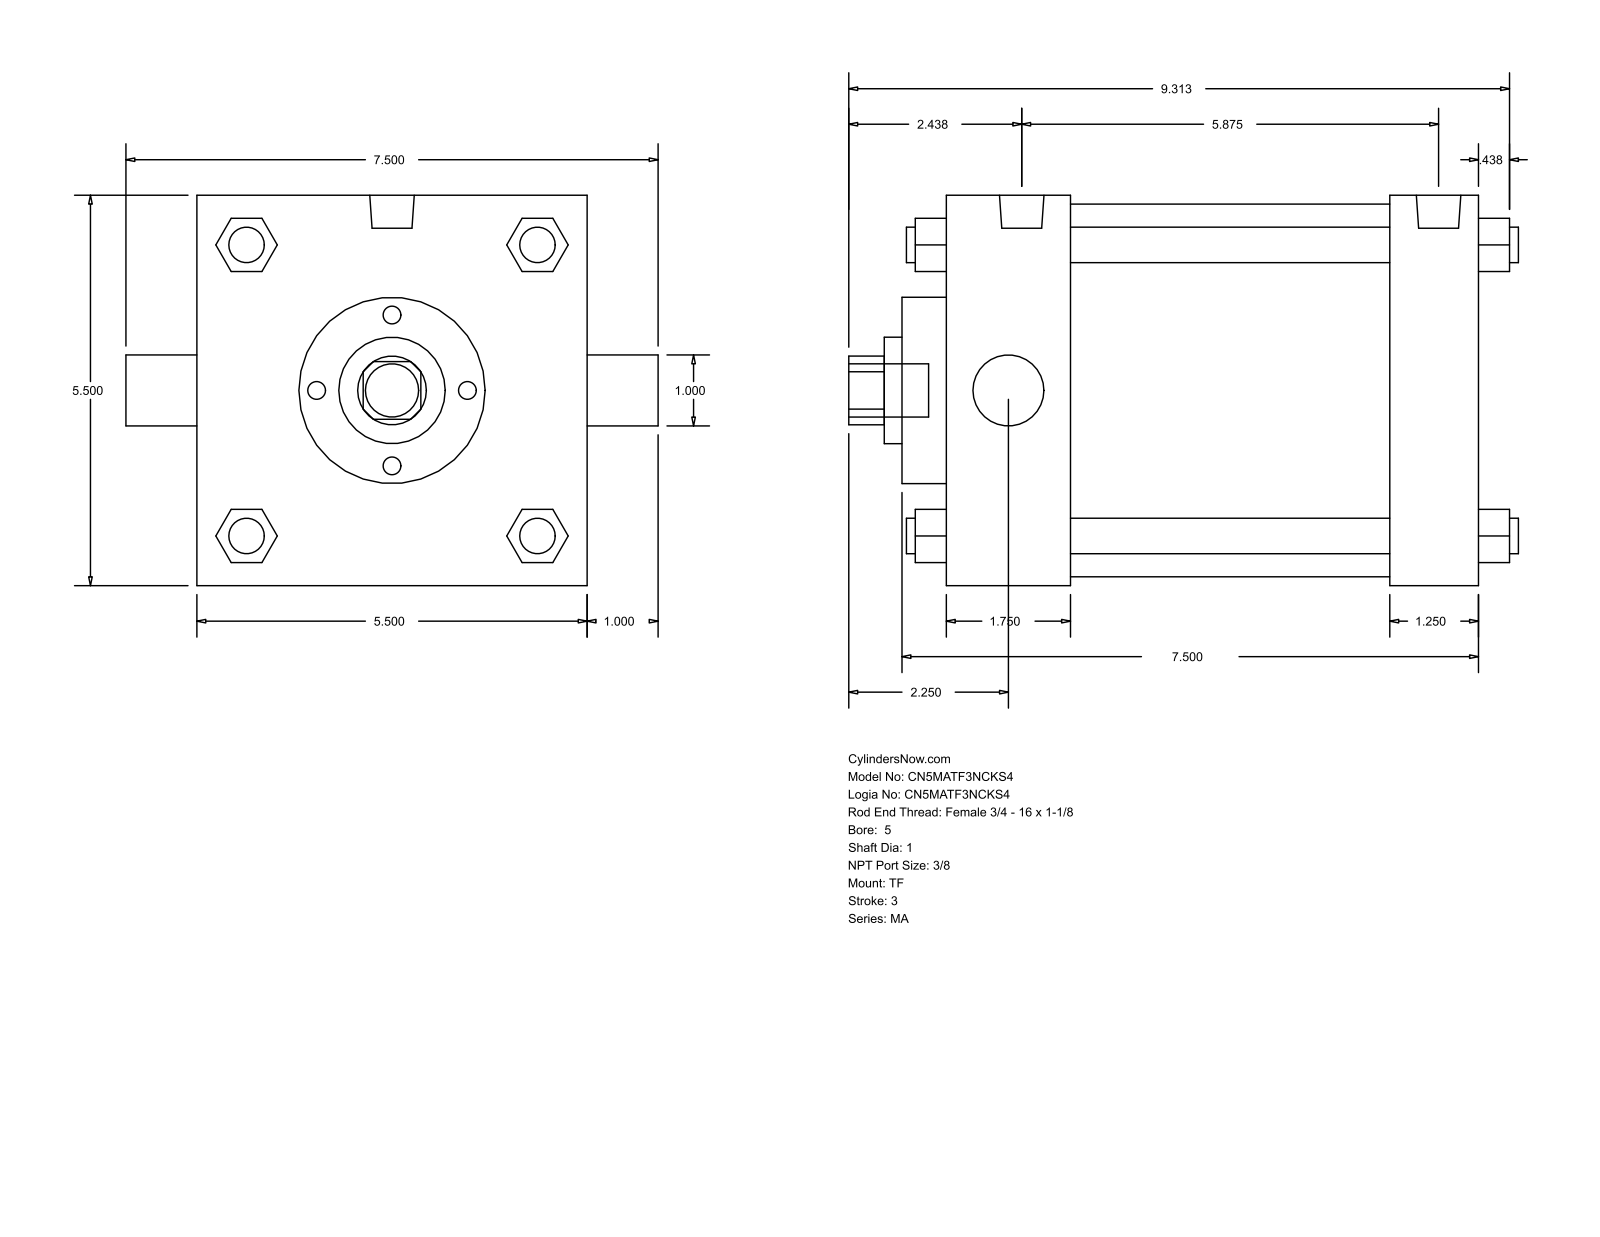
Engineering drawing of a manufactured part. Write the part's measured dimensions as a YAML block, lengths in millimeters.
part_name: "MA_TF__0500_1"
step_written_by: "GSSL Pune (CONFIG_CONTROL_DESIGN)"
units: millimeters
bodies: {solids: 0, faces: 122, planar: 93, cylindrical: 29, other: 0}
overall_size: [239.71, 190.5, 139.7]
round_holes:
  - {diameter: 25.4, count: 2}
  - {diameter: 38.1, count: 1}
  - {diameter: 66.67, count: 1}
  - {diameter: 133.35, count: 1}
round_bosses_or_shafts:
  - {diameter: 12.7, count: 4}
  - {diameter: 11.11, count: 3}
  - {diameter: 15.93, count: 2}
  - {diameter: 19.05, count: 1}
partial_cylinders:
  - {radius: 12.29, count: 1}
face_to_face_distances: [139.7, 190.51, 158.76, 31.75, 44.46, 114.3, 146.05, 15.87, 60.33, 174.63]
